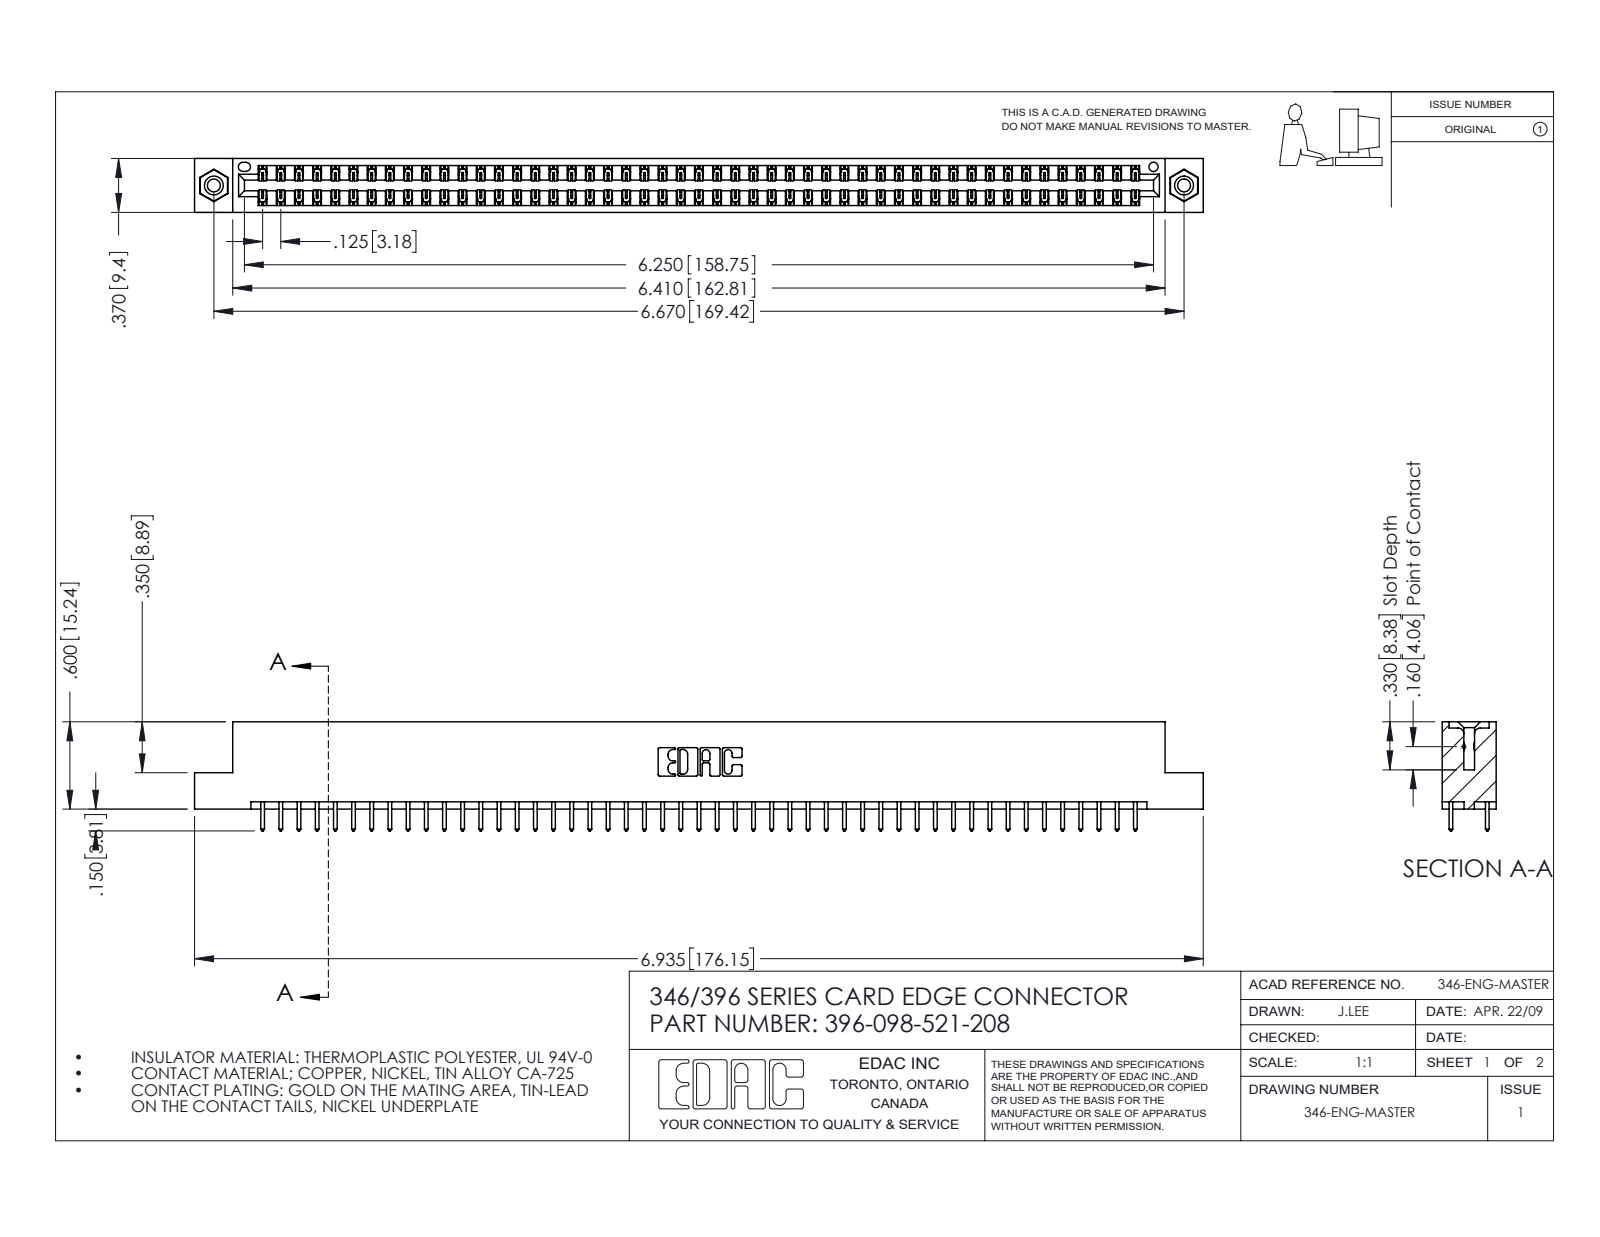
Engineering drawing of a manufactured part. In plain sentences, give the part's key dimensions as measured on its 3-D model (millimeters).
The part is named "345-292-001_345-293-121; 396-098-521-208; 345-250-001_345-250-003-102; 346 Part_Flush Mounting Lugs - 0.156 Dia-TI". Its 3-D file was written by "SolidWorks 2016 (CONFIG_CONTROL_DESIGN)". It is 101 solids with 5278 faces: 3538 planar, 1724 cylindrical and 16 other. Overall it measures 176.1 by 19.1 by 9.4 millimeters. Its volume is 17 190 cubic millimeters and its surface area 23 480 square millimeters. Round holes: 2 of diameter 2.3, 2 of diameter 3.2, 2 of diameter 4, 1 of diameter 1.6. Round bosses or shafts: 2 of diameter 3.9. Partial cylindrical surfaces (rounded edges, fillets, slot ends): 147 of radius 0.2, 98 of radius 0.3, 22 of radius 0.3, 6 of radius 0.2, 6 of radius 0.8, 3 of radius 0.7, 2 of radius 0.4, 2 of radius 0.6. The main face-to-face distances are 1.2, 8.2, 9.4, 6.4, 1.8, 7.6, 0.6, 7, 3.8, 5.6. The hole center spacings are 6.2, 164.1, 169.4.
